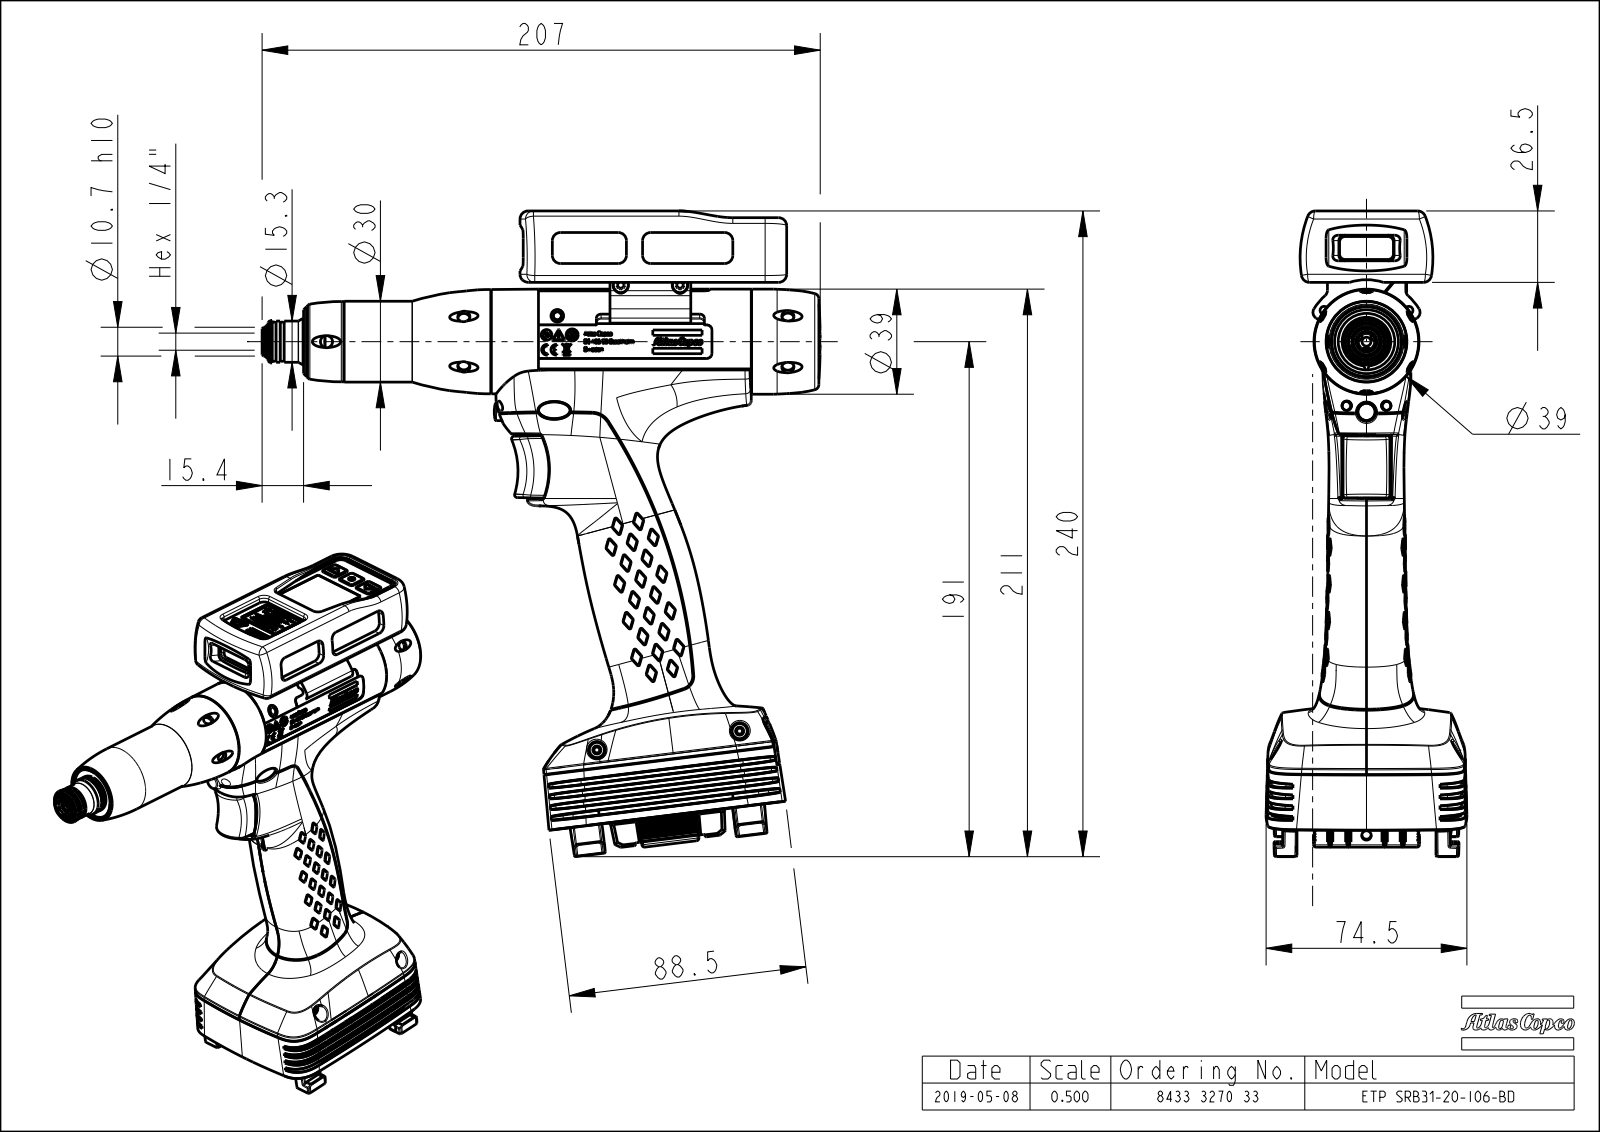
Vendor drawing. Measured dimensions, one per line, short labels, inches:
name: HANDLE_SW0001; TOP_SW0003; 8433327033_DIM_ASM
written by: CREO PARAMETRIC BY PTC INC, 2020281 (CONFIG_CONTROL_DESIGN)
unit: in
bodies: 3 solids, 5315 faces (1545 planar, 1338 cylindrical, 2432 other)
size: 9.433 × 8.158 × 2.935
volume: 41.52 in³; area: 170 in²
holes: 8× ⌀0.177, 4× ⌀0.256, 2× ⌀0.13, 2× ⌀0.138, 1× ⌀0.009, 1× ⌀0.016, 1× ⌀0.026, 1× ⌀0.118, 1× ⌀0.122, 1× ⌀0.157, 1× ⌀0.421
bosses: 5× ⌀0.22, 4× ⌀0.244, 2× ⌀0.15, 1× ⌀1.535, 1× ⌀1.524, 1× ⌀1.181, 1× ⌀1.173, 1× ⌀1.02
rounds: 341× R0.012, 238× R0.02, 37× R0.004, 35× R0.039, 31× R0.118, 30× R0.011, 30× R0.02, 22× R0.079
face distances: 1.496, 0.217, 1.28, 1.358, 0.157, 0.079, 0.138, 0.315, 2.323, 0.965
hole spacings: 4.736, 1.468, 1.575, 2.323, 2.807, 0.184, 0.203, 0.241
